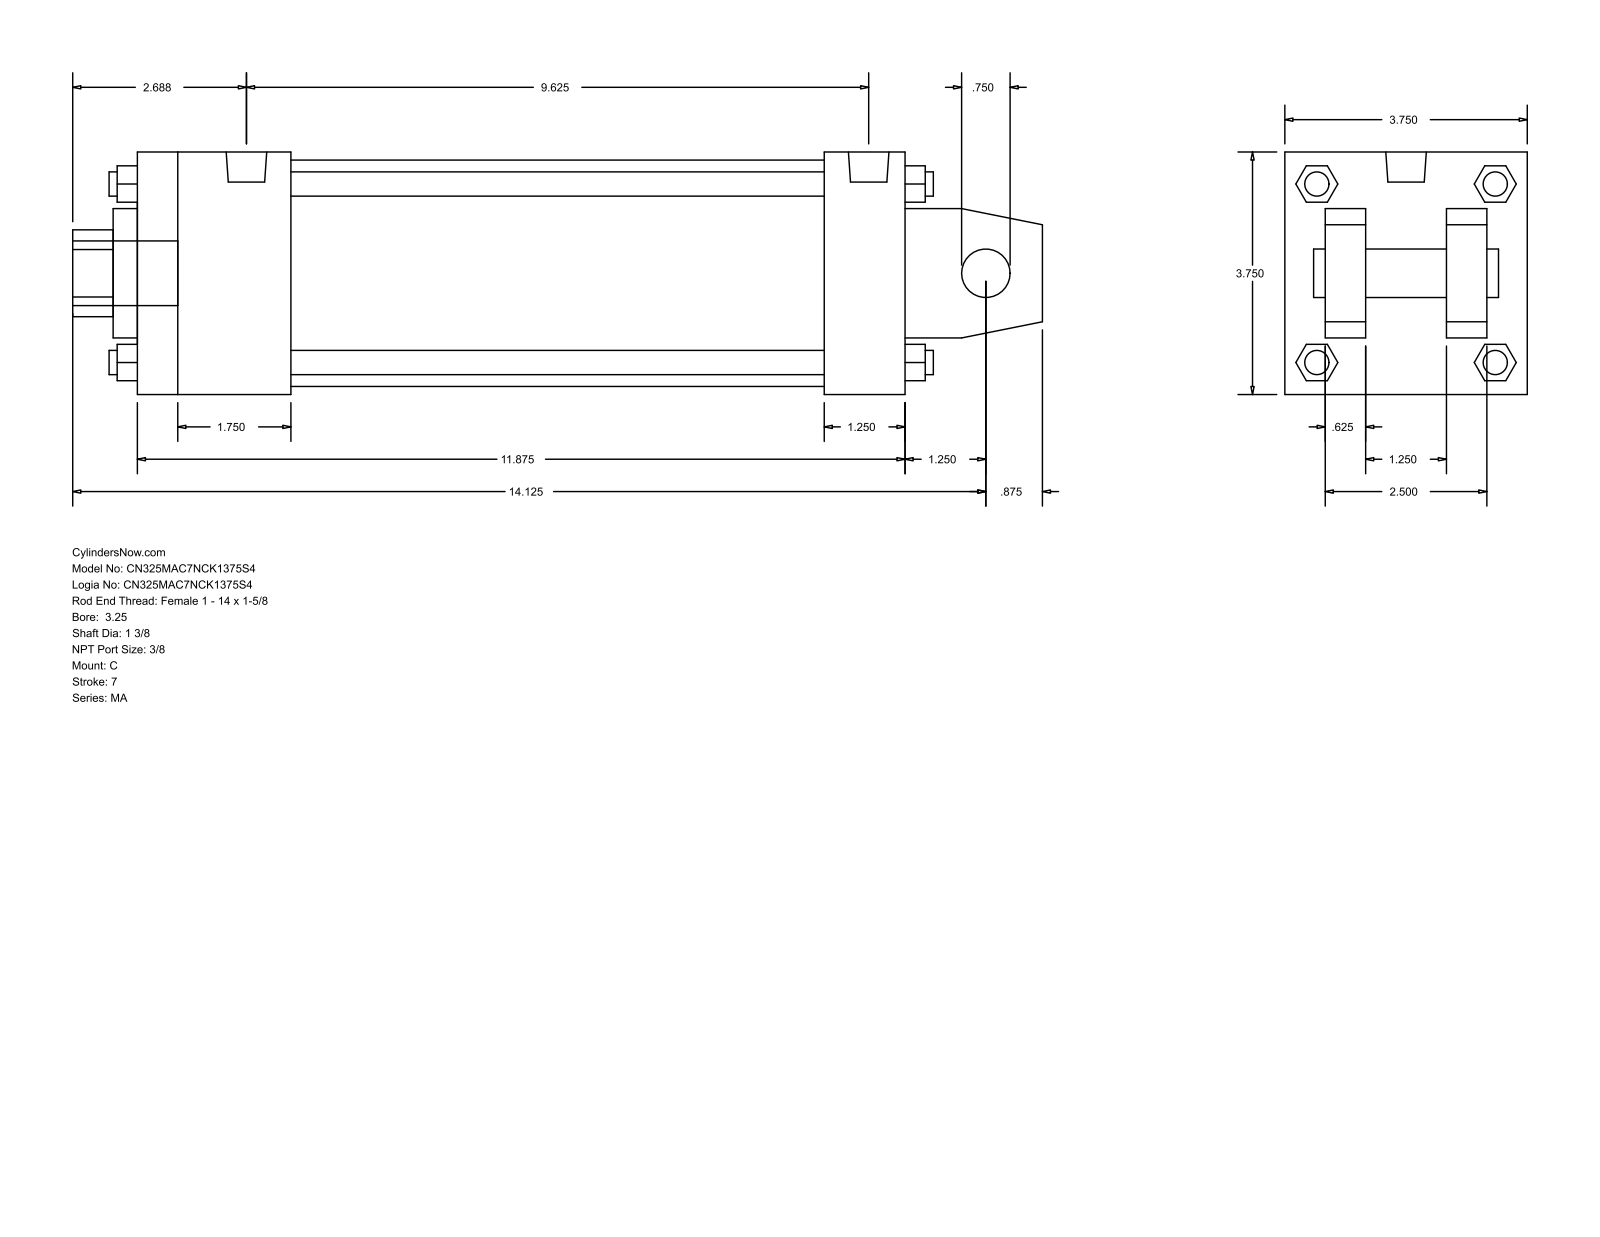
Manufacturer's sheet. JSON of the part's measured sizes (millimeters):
{"part_name": "MA_C__0325_1.375", "step_written_by": "GSSL Pune (CONFIG_CONTROL_DESIGN)", "units": "millimeters", "bodies": {"solids": 0, "faces": 139, "planar": 108, "cylindrical": 31, "other": 0}, "overall_size": [381, 95.25, 95.25], "round_holes": [[19.05, 1], [34.92, 1], [50.8, 1], [88.9, 1]], "round_bosses_or_shafts": [[11.11, 4], [9.53, 4], [15.93, 2], [25.4, 1]], "partial_cylinders_radius": [[17.06, 1]], "face_to_face_distances": [95.24, 15.87, 63.5, 301.62, 31.74, 79.37, 47.63, 269.87, 31.75, 60.32]}
